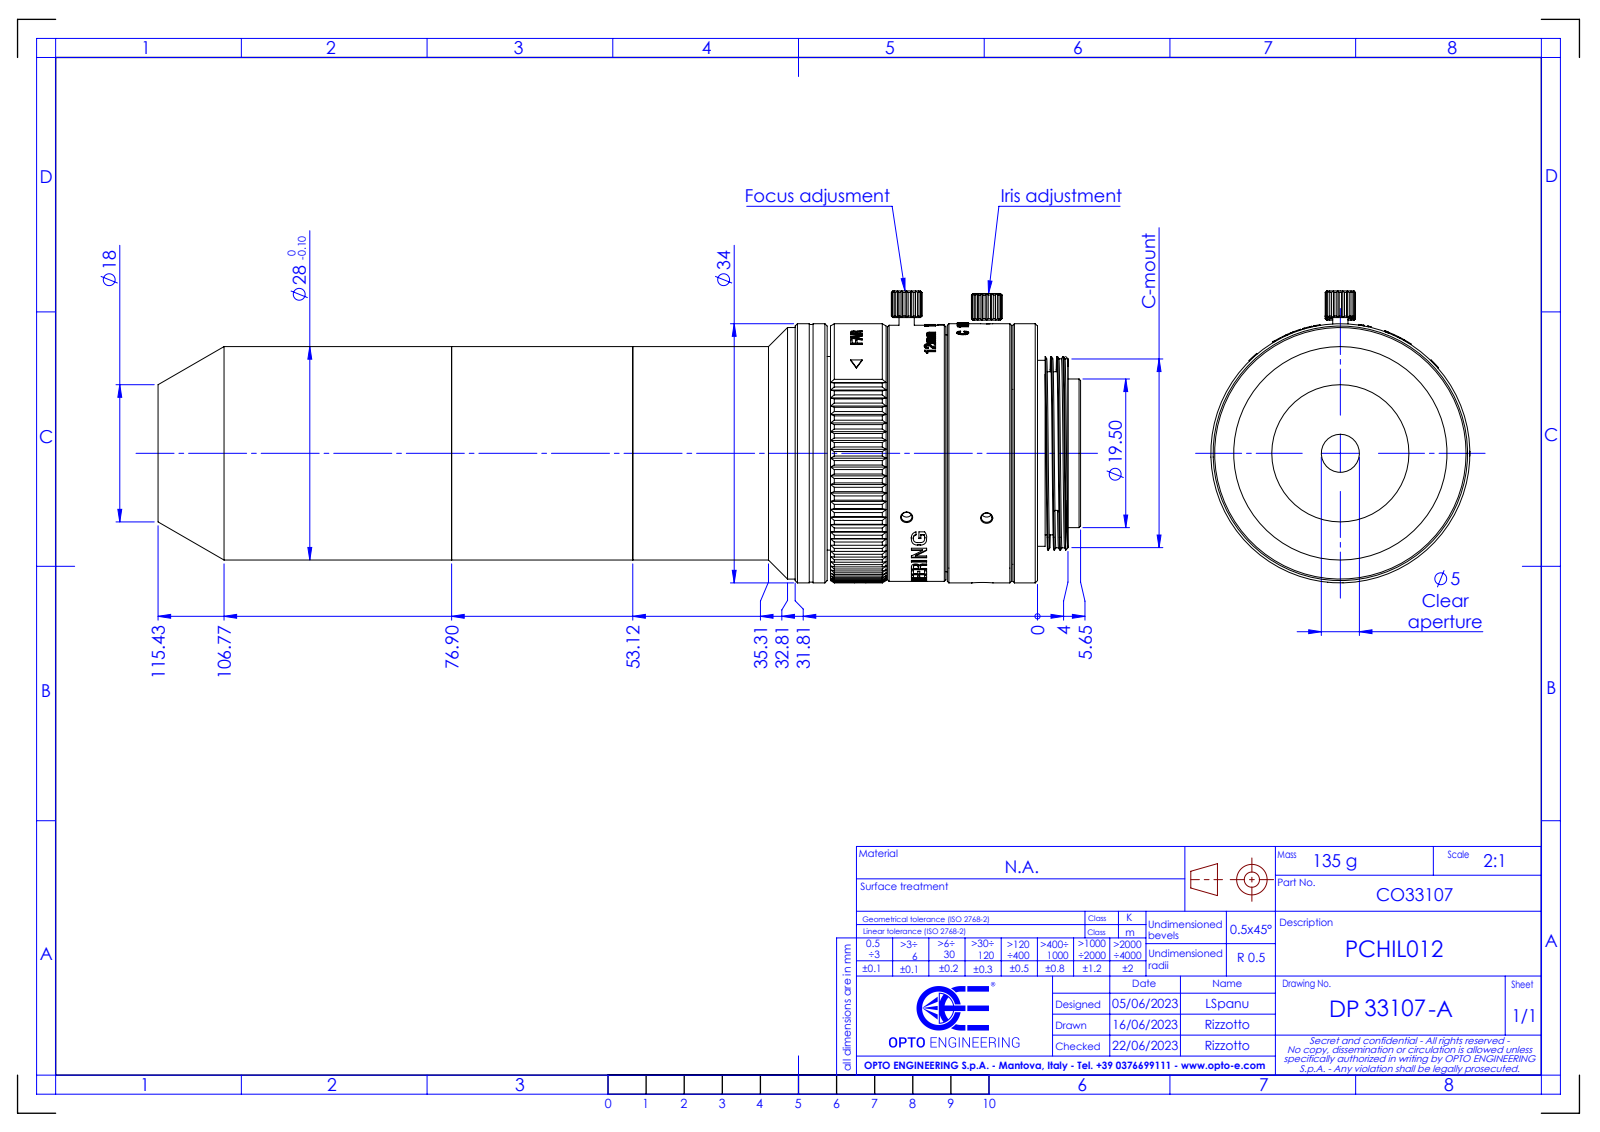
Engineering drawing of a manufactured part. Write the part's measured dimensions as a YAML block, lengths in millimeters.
part_name: "DP33107-A_PCHIL012"
step_written_by: "SolidWorks 2021 (CONFIG_CONTROL_DESIGN)"
units: millimeters
bodies: {solids: 0, faces: 754, planar: 309, cylindrical: 222, other: 223}
overall_size: [121.08, 38.3, 34]
round_holes:
  - {diameter: 1.4, count: 4}
  - {diameter: 2.1, count: 2}
  - {diameter: 2, count: 1}
  - {diameter: 2.6, count: 1}
  - {diameter: 5, count: 1}
  - {diameter: 11.8, count: 1}
  - {diameter: 21.4, count: 1}
  - {diameter: 31.08, count: 1}
  - {diameter: 32.6, count: 1}
round_bosses_or_shafts:
  - {diameter: 2, count: 3}
  - {diameter: 34, count: 1}
  - {diameter: 33.8, count: 1}
  - {diameter: 33.6, count: 1}
  - {diameter: 33, count: 1}
  - {diameter: 28, count: 1}
  - {diameter: 25.4, count: 1}
  - {diameter: 24.4, count: 1}
partial_cylinders:
  - {radius: 2, count: 2}
  - {radius: 16.7, count: 1}
  - {radius: 16.88, count: 1}
  - {radius: 17.08, count: 1}
  - {radius: 17.09, count: 1}
face_to_face_distances: [115.43, 86.62, 28.81, 38.53, 48.09, 76.9, 113.97, 75.44, 27.35, 1.46]
hole_center_spacings: [10.51, 13.95, 24.16]
